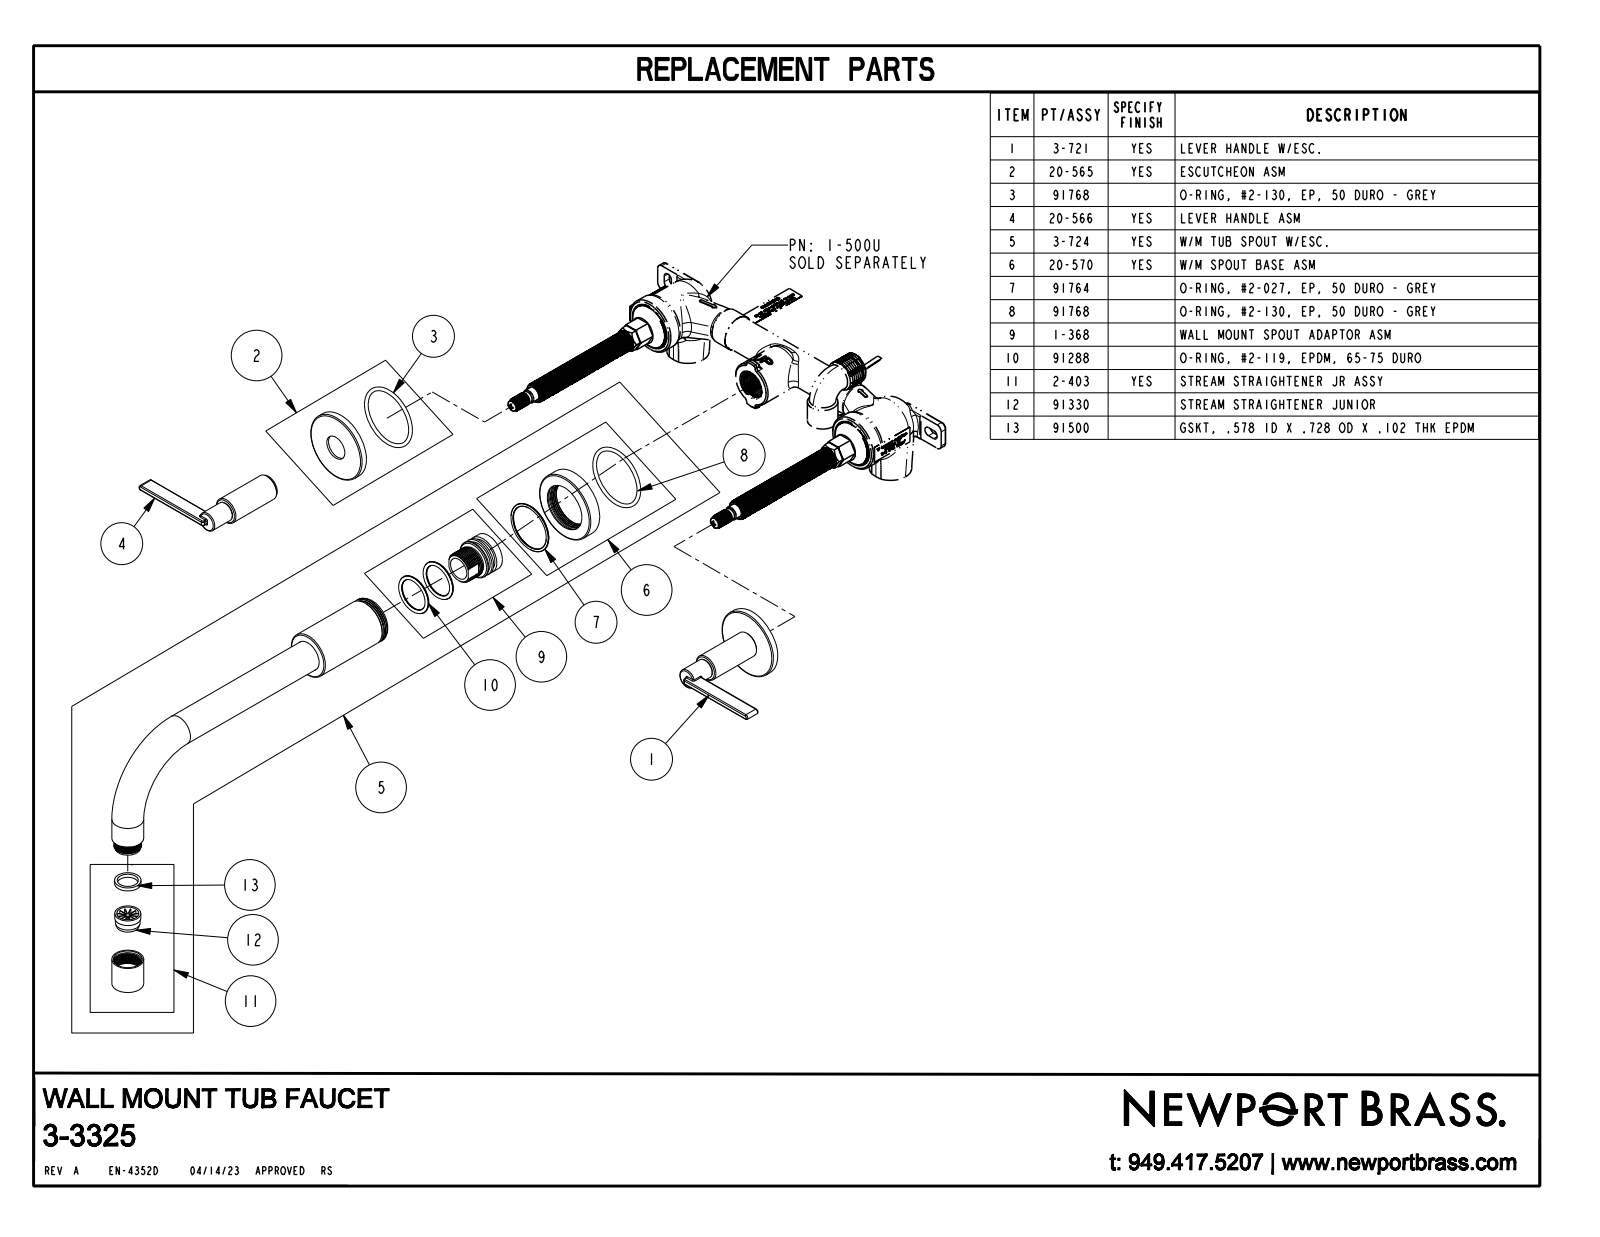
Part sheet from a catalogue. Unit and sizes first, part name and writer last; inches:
Units: inches
Overall size (bounding box): 12.875 × 10.44 × 8.687
Round holes (diameter × count): ⌀1.6 ×3, ⌀0.11 ×2, ⌀0.36 ×2, ⌀0.397 ×2, ⌀0.4 ×2, ⌀0.516 ×2, ⌀0.535 ×2, ⌀0.6 ×2, ⌀0.7 ×2, ⌀0.751 ×2, ⌀1.89 ×2, ⌀0.118 ×1
Round bosses / shafts (diameter × count): ⌀0.68 ×3, ⌀2 ×2, ⌀1.65 ×2, ⌀0.875 ×2, ⌀0.75 ×2, ⌀0.73 ×2, ⌀0.563 ×2, ⌀0.51 ×2
Partial cylindrical surfaces — rounded edges, fillets, slot ends (radius × count): R0.03 ×16, R0.06 ×2, R0.075 ×2, R0.137 ×2, R0.3 ×1
Main face-to-face distances: 0.05, 0.15, 0.295, 0.07, 0.12, 0.225, 0.175, 0.08, 0.2, 0.375
Hole centre spacings: 7.175, 7.178, 7.875
Volume: 5.708 in³ · Surface area: 122.2 in²
Bodies: 11 solids, 634 faces (188 planar, 299 cylindrical, 147 other)
Part name (STEP PRODUCT): 13532; 20-565_ASM; 13533; 13534 (+8 more)
STEP written by: CREO PARAMETRIC BY PTC INC, 2018400 (CONFIG_CONTROL_DESIGN)
